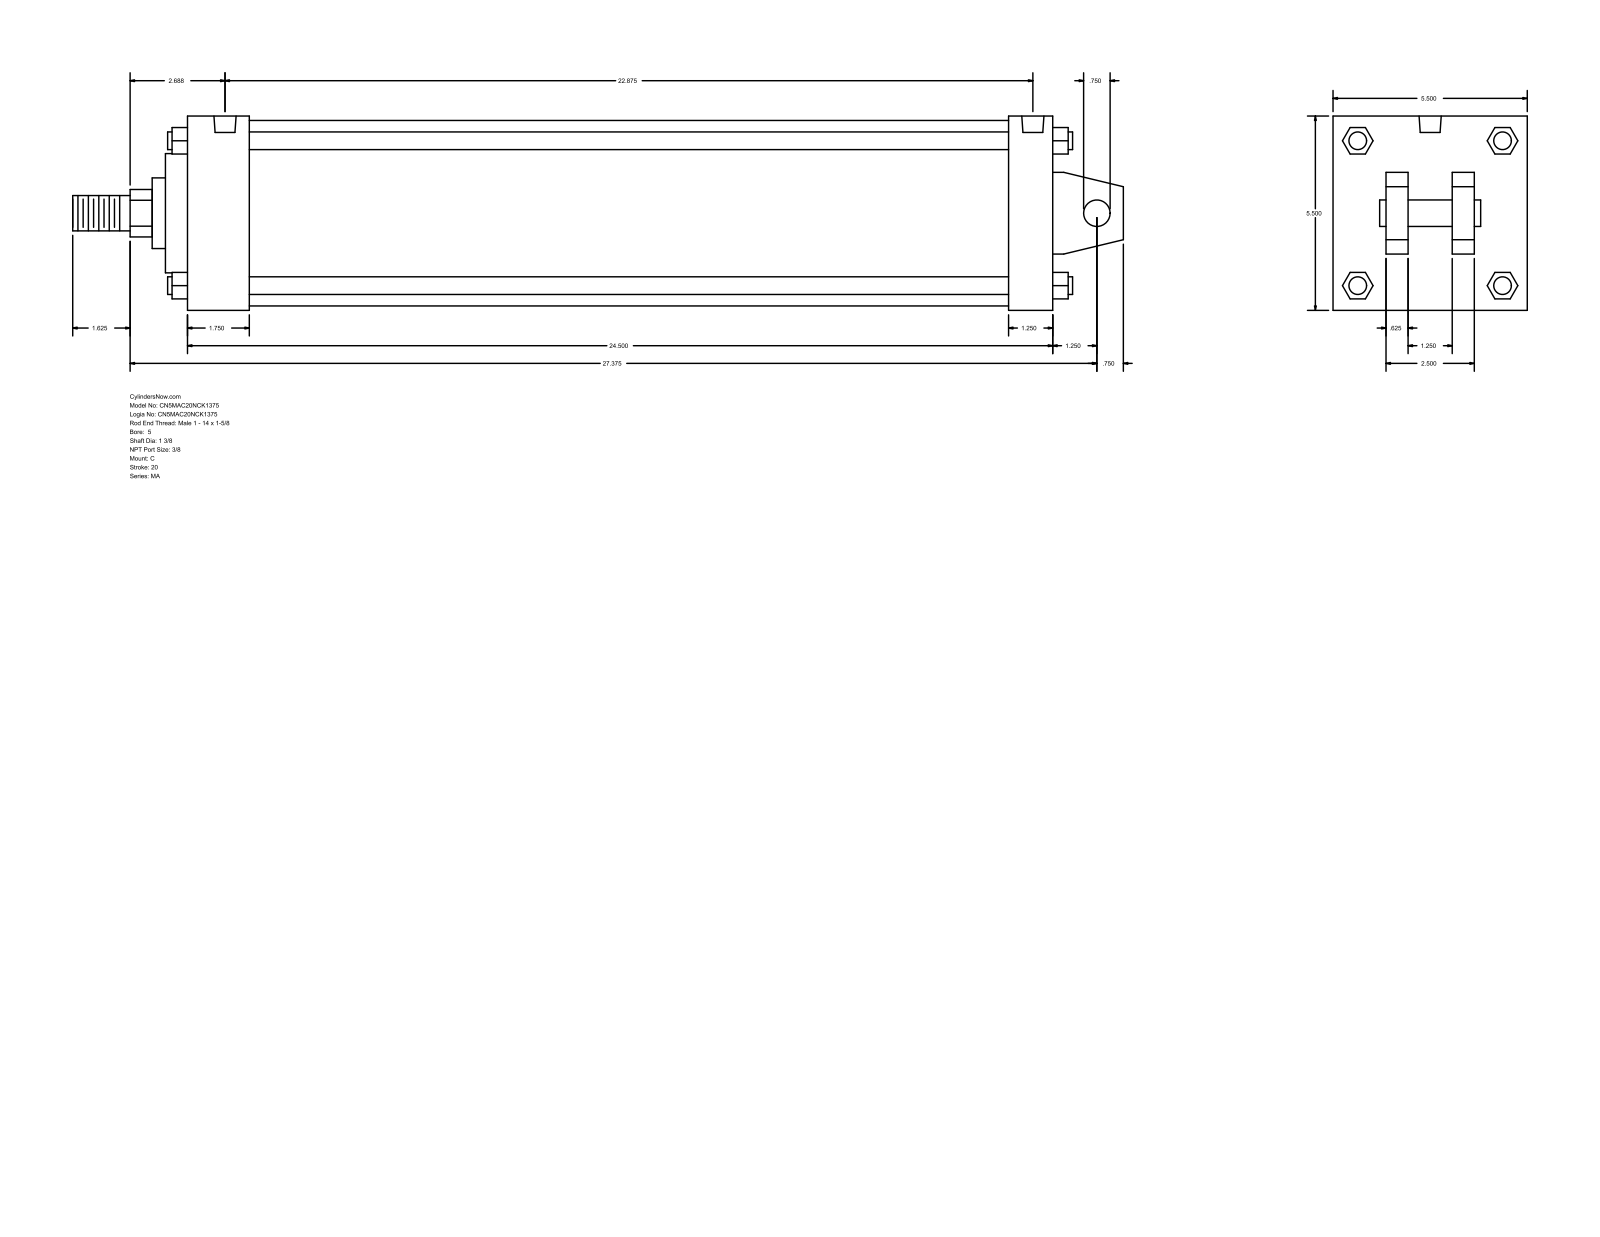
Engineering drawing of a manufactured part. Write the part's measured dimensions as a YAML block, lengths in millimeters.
part_name: "MA_C__0500_1.375"
step_written_by: "GSSL Pune (CONFIG_CONTROL_DESIGN)"
units: millimeters
bodies: {solids: 0, faces: 141, planar: 109, cylindrical: 32, other: 0}
overall_size: [755.65, 139.7, 139.7]
round_holes:
  - {diameter: 11.11, count: 4}
  - {diameter: 15.93, count: 2}
round_bosses_or_shafts:
  - {diameter: 12.7, count: 4}
  - {diameter: 133.35, count: 1}
  - {diameter: 85.72, count: 1}
  - {diameter: 50.8, count: 1}
  - {diameter: 34.92, count: 1}
  - {diameter: 25.4, count: 1}
  - {diameter: 19.05, count: 1}
partial_cylinders:
  - {radius: 17.06, count: 1}
face_to_face_distances: [139.7, 622.31, 15.87, 590.56, 31.75, 44.45, 546.11, 577.86, 53.97, 38.1]
hole_center_spacings: [4.77, 571.49, 576.26, 581.03]
